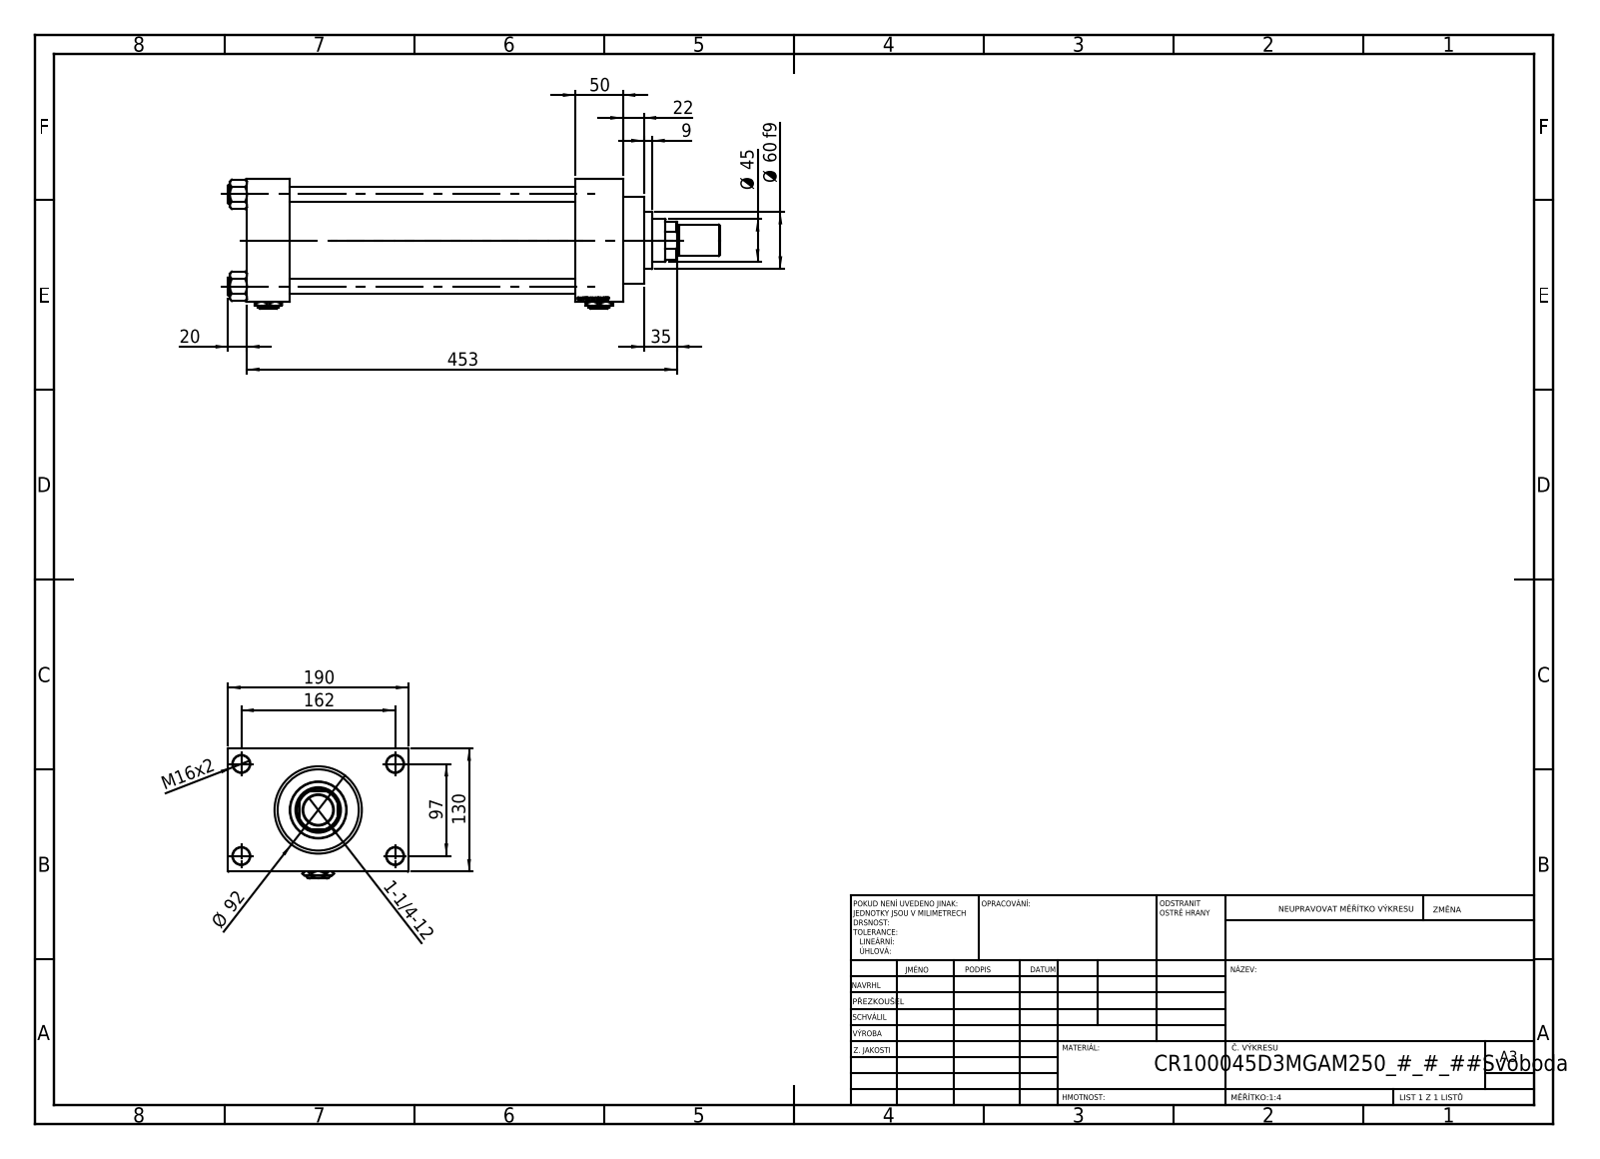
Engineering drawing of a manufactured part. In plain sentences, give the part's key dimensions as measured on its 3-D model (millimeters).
The part is named "Zatka_pro_OIL_PORT; V215_VC_A; V215CR_VCP_D; NUT_M5_D (+3 more)". Its 3-D file was written by "SolidWorks 2019 (CONFIG_CONTROL_DESIGN)". It is 14 solids with 1267 faces: 597 planar, 104 cylindrical and 566 other. Overall it measures 518 by 190 by 137 millimeters. Its volume is 3 405 000 cubic millimeters and its surface area 593 384 square millimeters. Round holes: 4 of diameter 16, 4 of diameter 18, 2 of diameter 7, 2 of diameter 26.44, 2 of diameter 35, 1 of diameter 31.5, 1 of diameter 45, 1 of diameter 48, 1 of diameter 76, 1 of diameter 85.5, 1 of diameter 100. Round bosses or shafts: 4 of diameter 19, 1 of diameter 106, 1 of diameter 92, 1 of diameter 60, 1 of diameter 33, 1 of diameter 31. Partial cylindrical surfaces (rounded edges, fillets, slot ends): 1 of radius 22. The main face-to-face distances are 45, 130, 346, 301, 396, 351, 50, 30, 160, 190. The hole center spacings are 32.55, 68.52, 94.41, 96.9, 102.27, 129.45, 161.73, 97.
